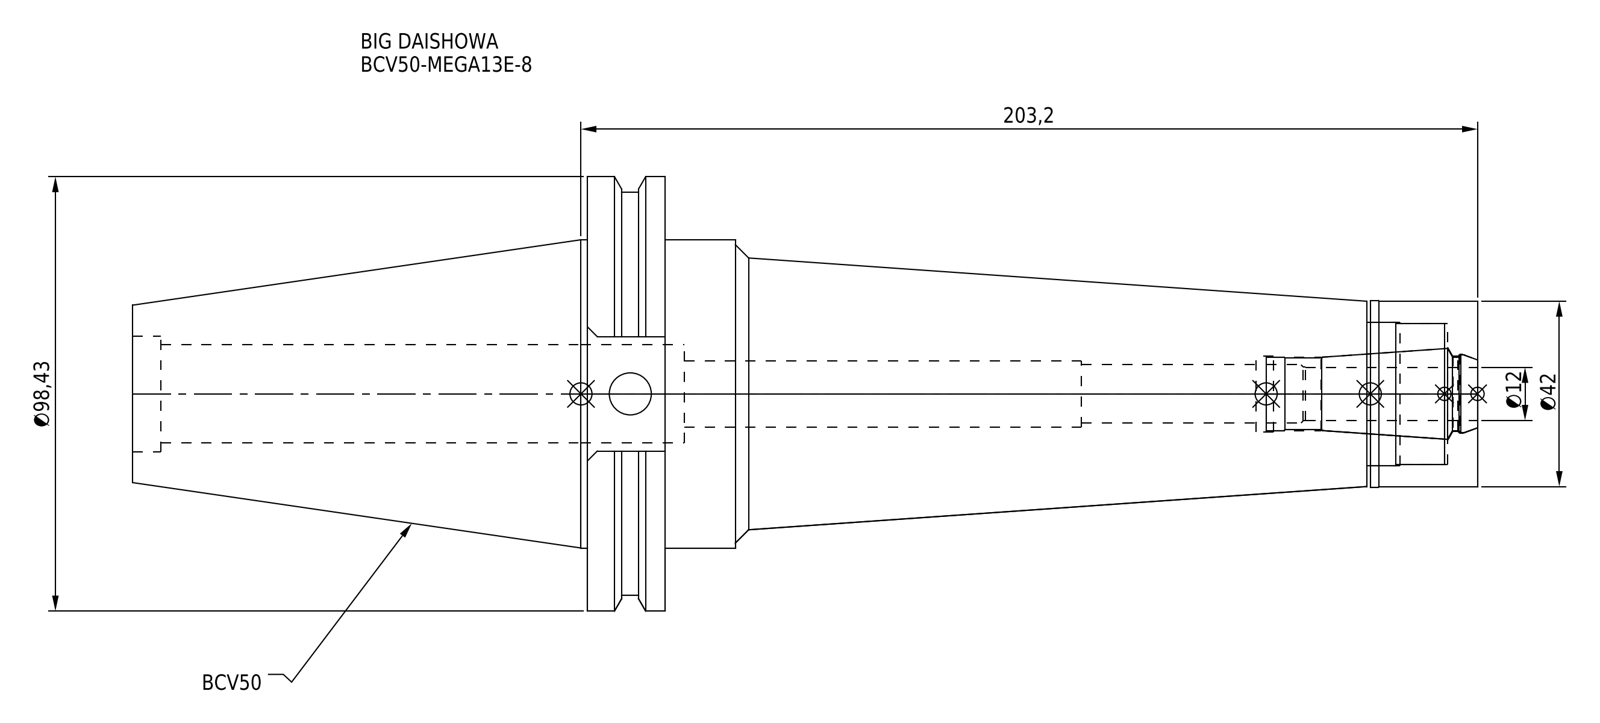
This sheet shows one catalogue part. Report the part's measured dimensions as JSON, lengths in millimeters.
{"part_name": "BCV50ME13080-120_ASM.stp; DXF_TEMP_ASSY_ASM_4_ASM.stp; BCV50-MEGA13E-8-120-FreeParts; BCV50-MEGA13E-8_1.stp (+3 more)", "step_written_by": "SolidWorks 2019 (CONFIG_CONTROL_DESIGN)", "units": "millimeters", "bodies": {"solids": 2, "faces": 93, "planar": 31, "cylindrical": 42, "other": 20}, "overall_size": [304.8, 98.42, 94.95], "volume_mm3": 690968, "surface_area_mm2": 87870, "round_holes": [[9.53, 1], [13.3, 1], [15, 1], [16.6, 1], [17, 1], [17.2, 1], [17.9, 1], [22.3, 1], [26.23, 1], [32, 1], [32.5, 1]], "round_bosses_or_shafts": [[98.42, 1], [91.29, 1], [69.85, 1], [42.3, 1], [42, 1]], "face_to_face_distances": [17.55, 184.15, 201.7, 304.8, 120.65, 103.1, 25.1, 24.3, 159.85, 177.4]}
